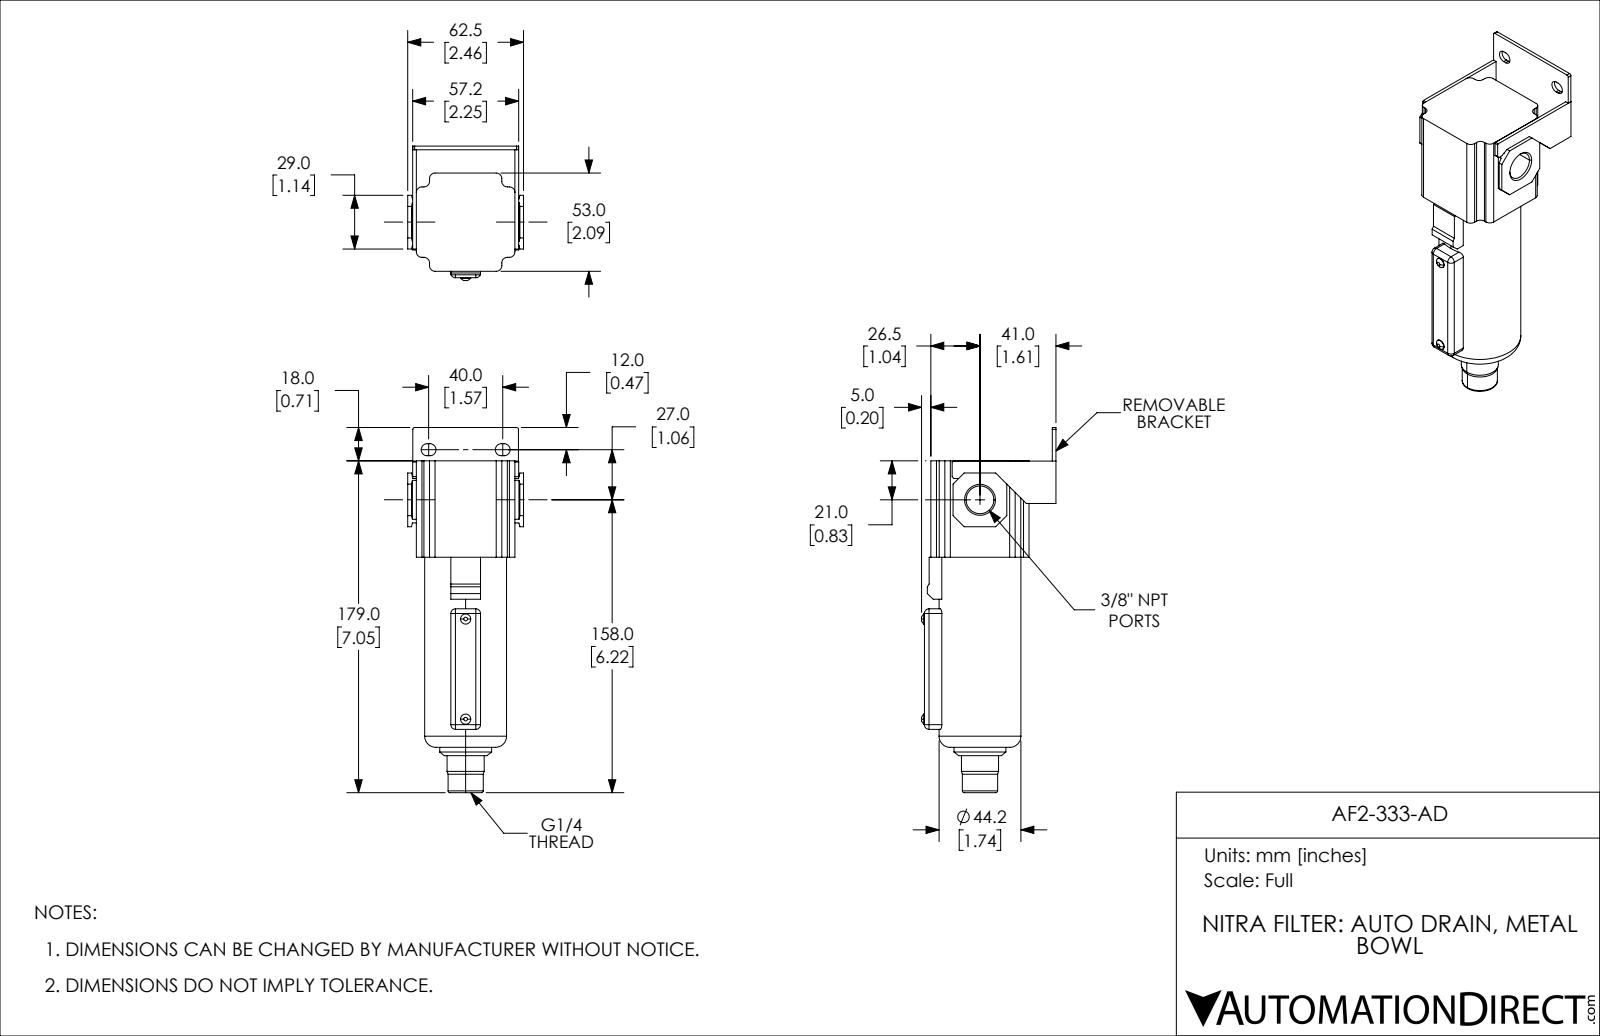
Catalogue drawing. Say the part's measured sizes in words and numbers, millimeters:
The part is named "AF2-333-AD". Its 3-D file was written by "SolidWorks 2019 (CONFIG_CONTROL_DESIGN)". It is 1 solid with 161 faces: 95 planar, 44 cylindrical and 22 other. Overall it measures 197 by 72.5 by 62.5 millimeters. Its volume is 318 278 cubic millimeters and its surface area 42 642 square millimeters. Round holes: 1 of diameter 8.57, 1 of diameter 14.95. Round bosses or shafts: 2 of diameter 5.5, 1 of diameter 44.2, 1 of diameter 28, 1 of diameter 20, 1 of diameter 19. Partial cylindrical surfaces (rounded edges, fillets, slot ends): 12 of radius 3, 8 of radius 2.5, 4 of radius 3.25, 2 of radius 1. The main face-to-face distances are 2, 12.5, 14.5, 67.5, 65.5, 53, 55.2, 53.2, 20.6, 36.6.
